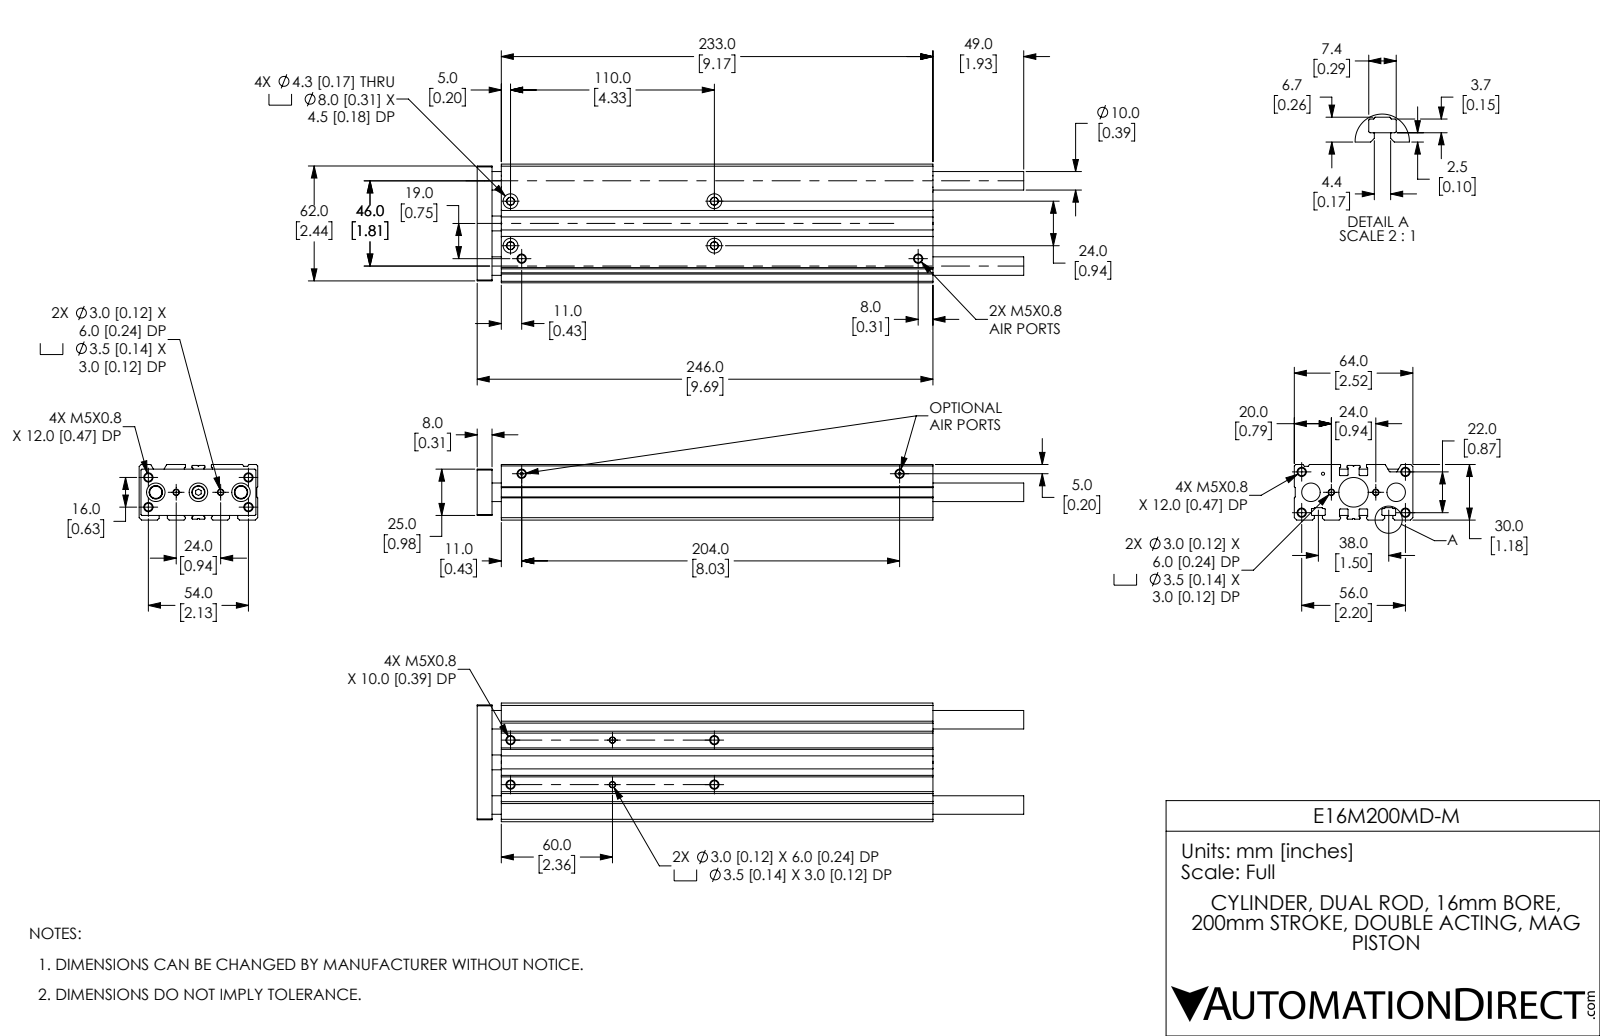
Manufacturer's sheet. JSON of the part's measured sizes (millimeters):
{"part_name": "E16M200MD-M_BODY; E16M200MD-M_ENDPLATE; E16M200MD-M", "step_written_by": "SolidWorks 2019 (CONFIG_CONTROL_DESIGN)", "units": "millimeters", "bodies": {"solids": 5, "faces": 411, "planar": 133, "cylindrical": 192, "other": 86}, "overall_size": [295, 64, 30], "volume_mm3": 380529, "surface_area_mm2": 127969, "round_holes": [[4.13, 16], [3, 4], [3.5, 4], [4.3, 4], [8, 4], [1.67, 3], [5, 3], [10, 3], [7.11, 2], [10, 1], [16, 1], [16, 1]], "round_bosses_or_shafts": [[8, 1], [7.11, 1]], "partial_cylinders_radius": [[0.2, 22], [0.4, 20], [0.25, 8], [0.3, 6], [0.5, 4]], "face_to_face_distances": [30, 0.5, 6, 64, 29, 24.4, 24, 35, 3.5, 39.6], "hole_center_spacings": [3.16, 8.94, 12.08, 17, 19.03, 19.42, 24, 28.16]}
